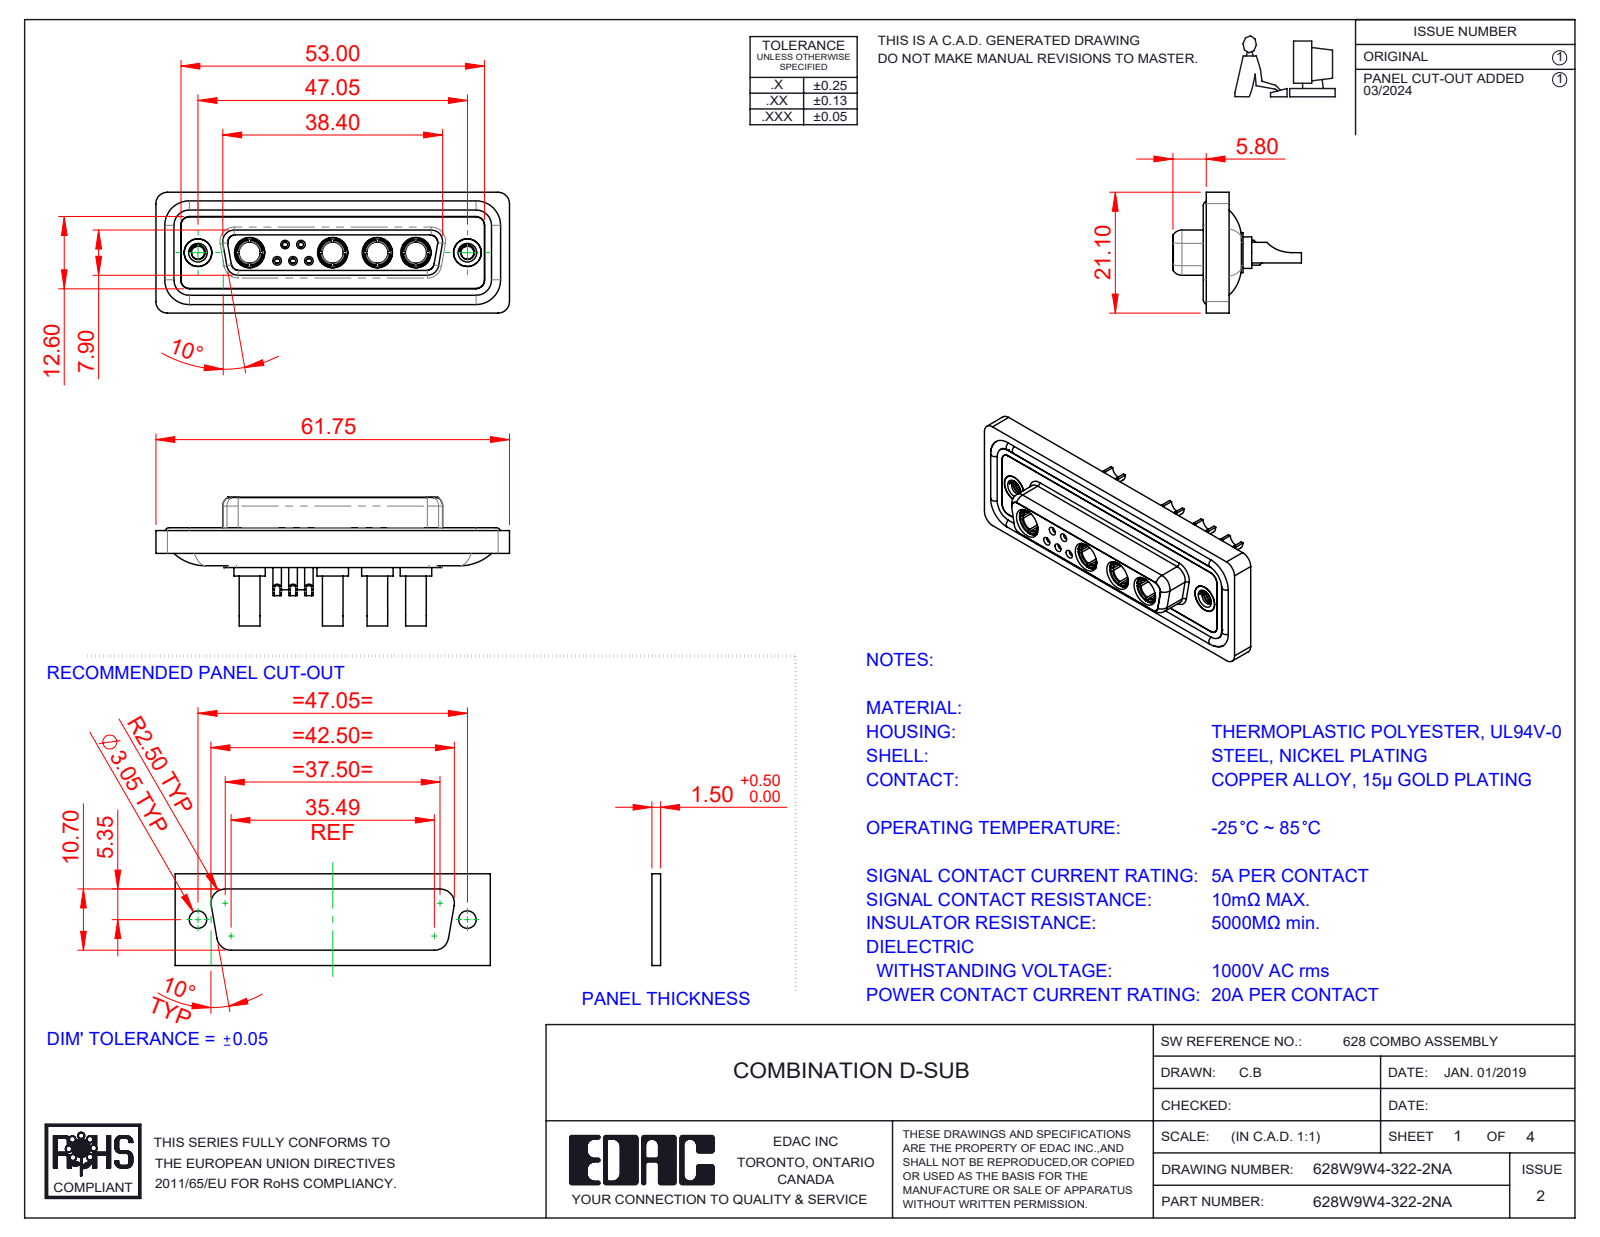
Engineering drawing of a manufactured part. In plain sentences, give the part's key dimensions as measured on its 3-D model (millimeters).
The part is named "628Combo Contact Row 1_22; Power Socket_20A SC; 628Combo Shell Front_25 Contacts; 628W9W4-322-2NA (+5 more)". Its 3-D file was written by "SolidWorks 2023 (CONFIG_CONTROL_DESIGN)". It is 20 solids with 979 faces: 318 planar, 399 cylindrical and 262 other. Overall it measures 61.75 by 22.45 by 21.1 millimeters. Its volume is 8 287 cubic millimeters and its surface area 13 944 square millimeters. Round holes: 6 of diameter 4.85, 5 of diameter 0.9, 5 of diameter 1, 5 of diameter 1.1, 5 of diameter 1.5, 5 of diameter 2, 4 of diameter 2.7, 4 of diameter 3.7, 4 of diameter 5.3, 3 of diameter 1.6, 2 of diameter 1.7, 2 of diameter 2.26. Round bosses or shafts: 6 of diameter 1.6, 5 of diameter 2.2, 4 of diameter 5.5, 4 of diameter 5.2, 4 of diameter 4.96, 4 of diameter 4.75, 4 of diameter 3.75, 4 of diameter 3.6. Partial cylindrical surfaces (rounded edges, fillets, slot ends): 22 of radius 1.5, 18 of radius 2, 8 of radius 1.35, 8 of radius 1.6, 6 of radius 1, 4 of radius 0.25, 4 of radius 0.5, 4 of radius 0.6. The main face-to-face distances are 0.4, 1.8, 7.45, 5.65, 0.5, 7.05, 6.6, 1.6, 1.1, 2.9. The hole center spacings are 3.16, 2.77, 5.03, 2.76, 4.4, 5.02, 5.54, 5.73.
